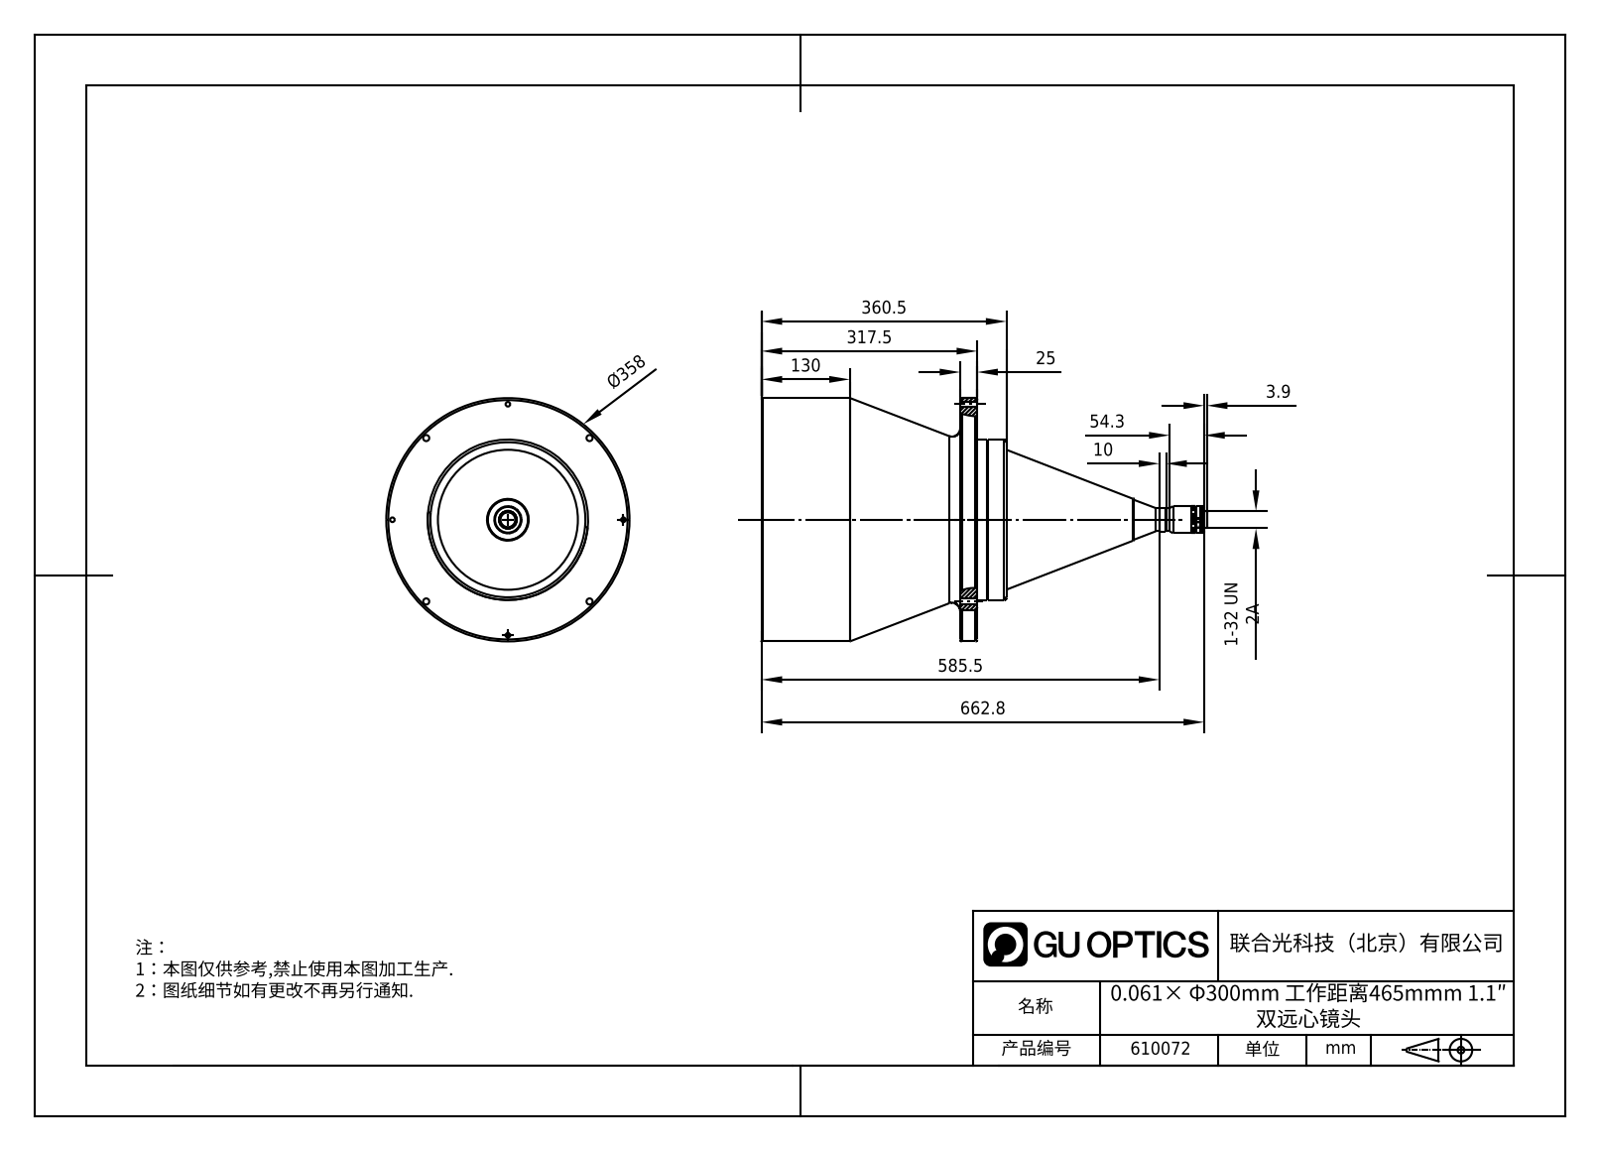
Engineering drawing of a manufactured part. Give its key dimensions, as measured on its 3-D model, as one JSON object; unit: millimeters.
{"part_name": "DTCM111-300S-AL", "step_written_by": "SolidWorks 2017 (CONFIG_CONTROL_DESIGN)", "units": "millimeters", "bodies": {"solids": 1, "faces": 261, "planar": 23, "cylindrical": 149, "other": 89}, "overall_size": [666.63, 358, 358], "volume_mm3": 31560000, "surface_area_mm2": 692478, "round_holes": [[6.8, 4], [9, 4], [2.5, 3], [22, 1], [206, 1], [340, 1]], "round_bosses_or_shafts": [[358, 1], [236, 1], [40, 1], [35, 1], [34, 1], [32.53, 1], [25.4, 1]], "partial_cylinders_radius": [[3, 26], [2, 24], [4, 7], [2.15, 4], [1.02, 1], [1.4, 1], [2.4, 1]], "face_to_face_distances": [25, 68, 43, 292.5, 317.5, 360.5, 662.83, 370.33, 345.33, 302.33], "hole_center_spacings": [130.11, 170, 240.42, 314.12, 340, 340.01]}
